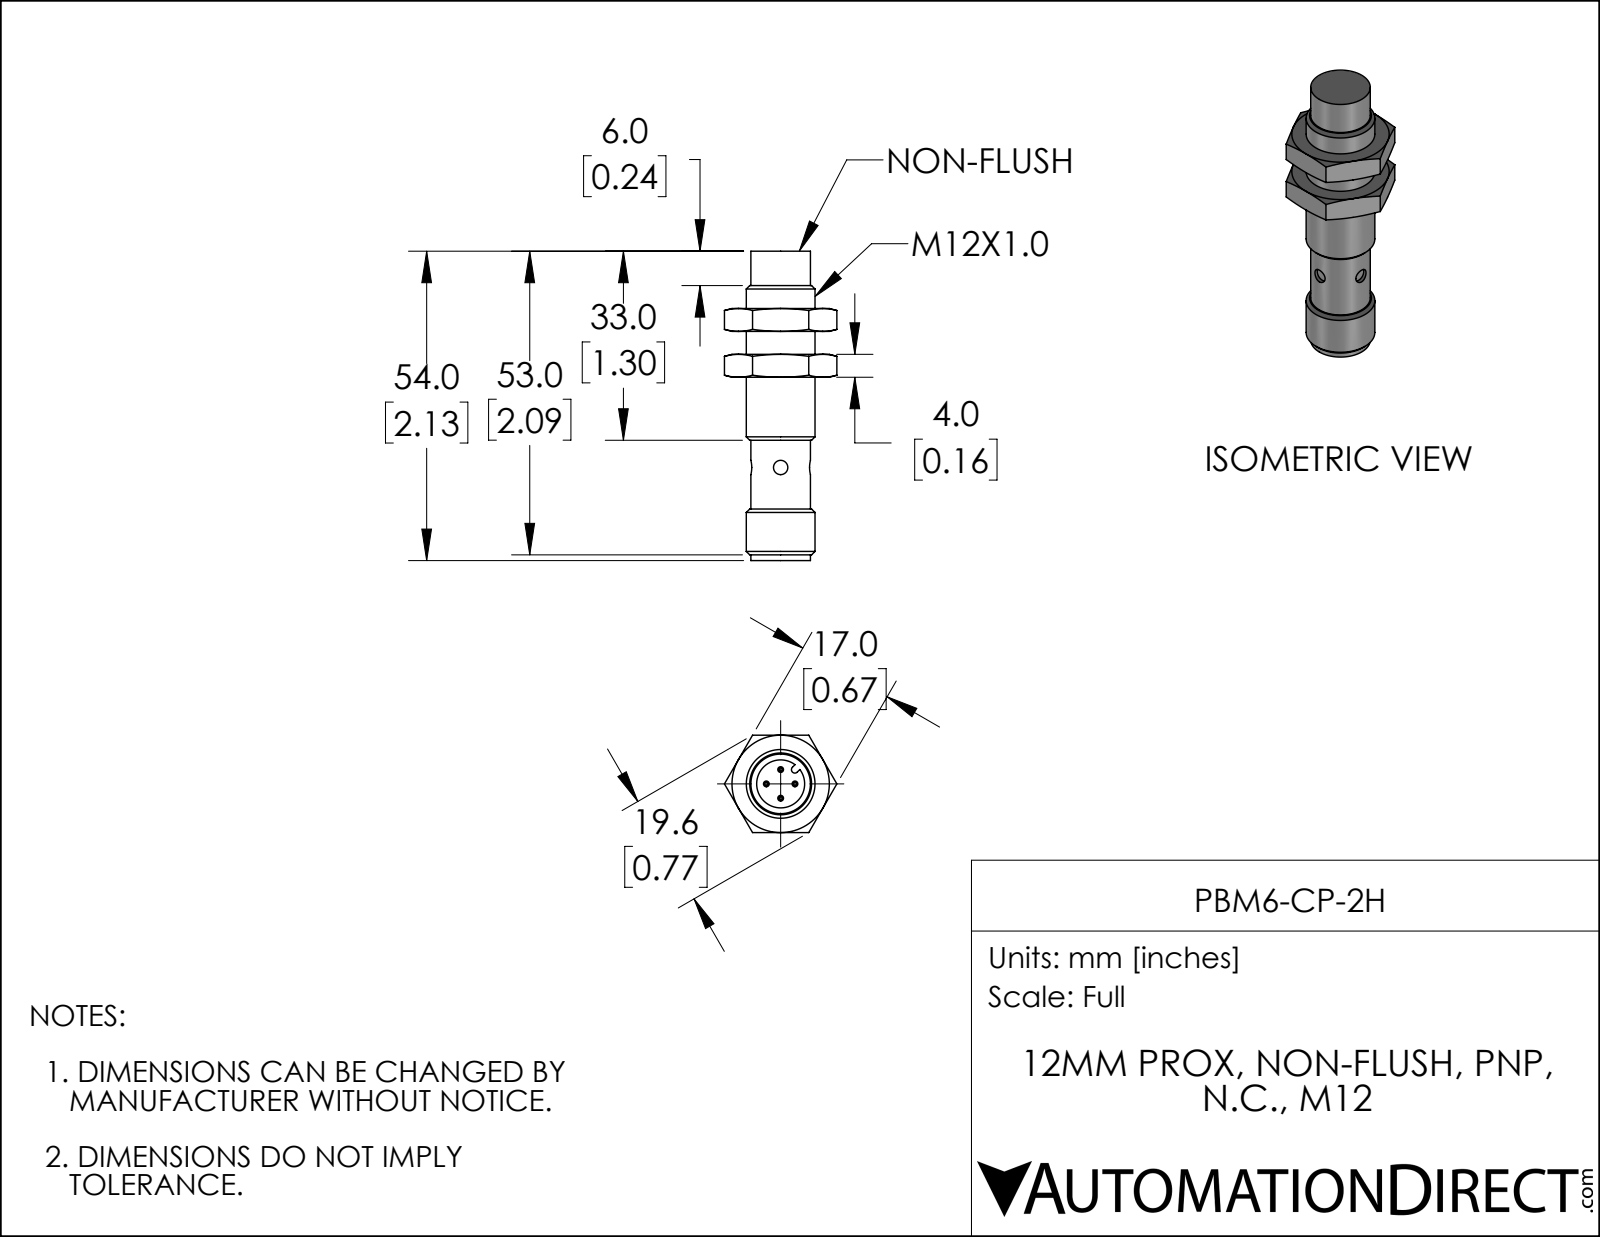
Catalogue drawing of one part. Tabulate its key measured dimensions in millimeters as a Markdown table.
| quantity | value |
| --- | --- |
| part name | DSD-0279 |
| STEP written by | SolidWorks 2019 (AUTOMOTIVE_DESIGN) |
| units | millimeters |
| bodies | 1 solid, 40 faces (17 planar, 15 cylindrical, 8 other) |
| overall size | 54 × 12 × 12 |
| volume | 5 080 mm³ |
| surface area | 2 532 mm² |
| round holes (diameter × count) | 2.5 × 2, 8.4 × 1 |
| round bosses / shafts (diameter × count) | 1 × 4, 12 × 1, 10.4 × 1 |
| partial cylindrical surfaces (radius × count) | 0.6 × 1 |
| main face-to-face distances | 45.1, 54, 8.9, 9, 33, 12.1, 21, 45, 12, 6 |
